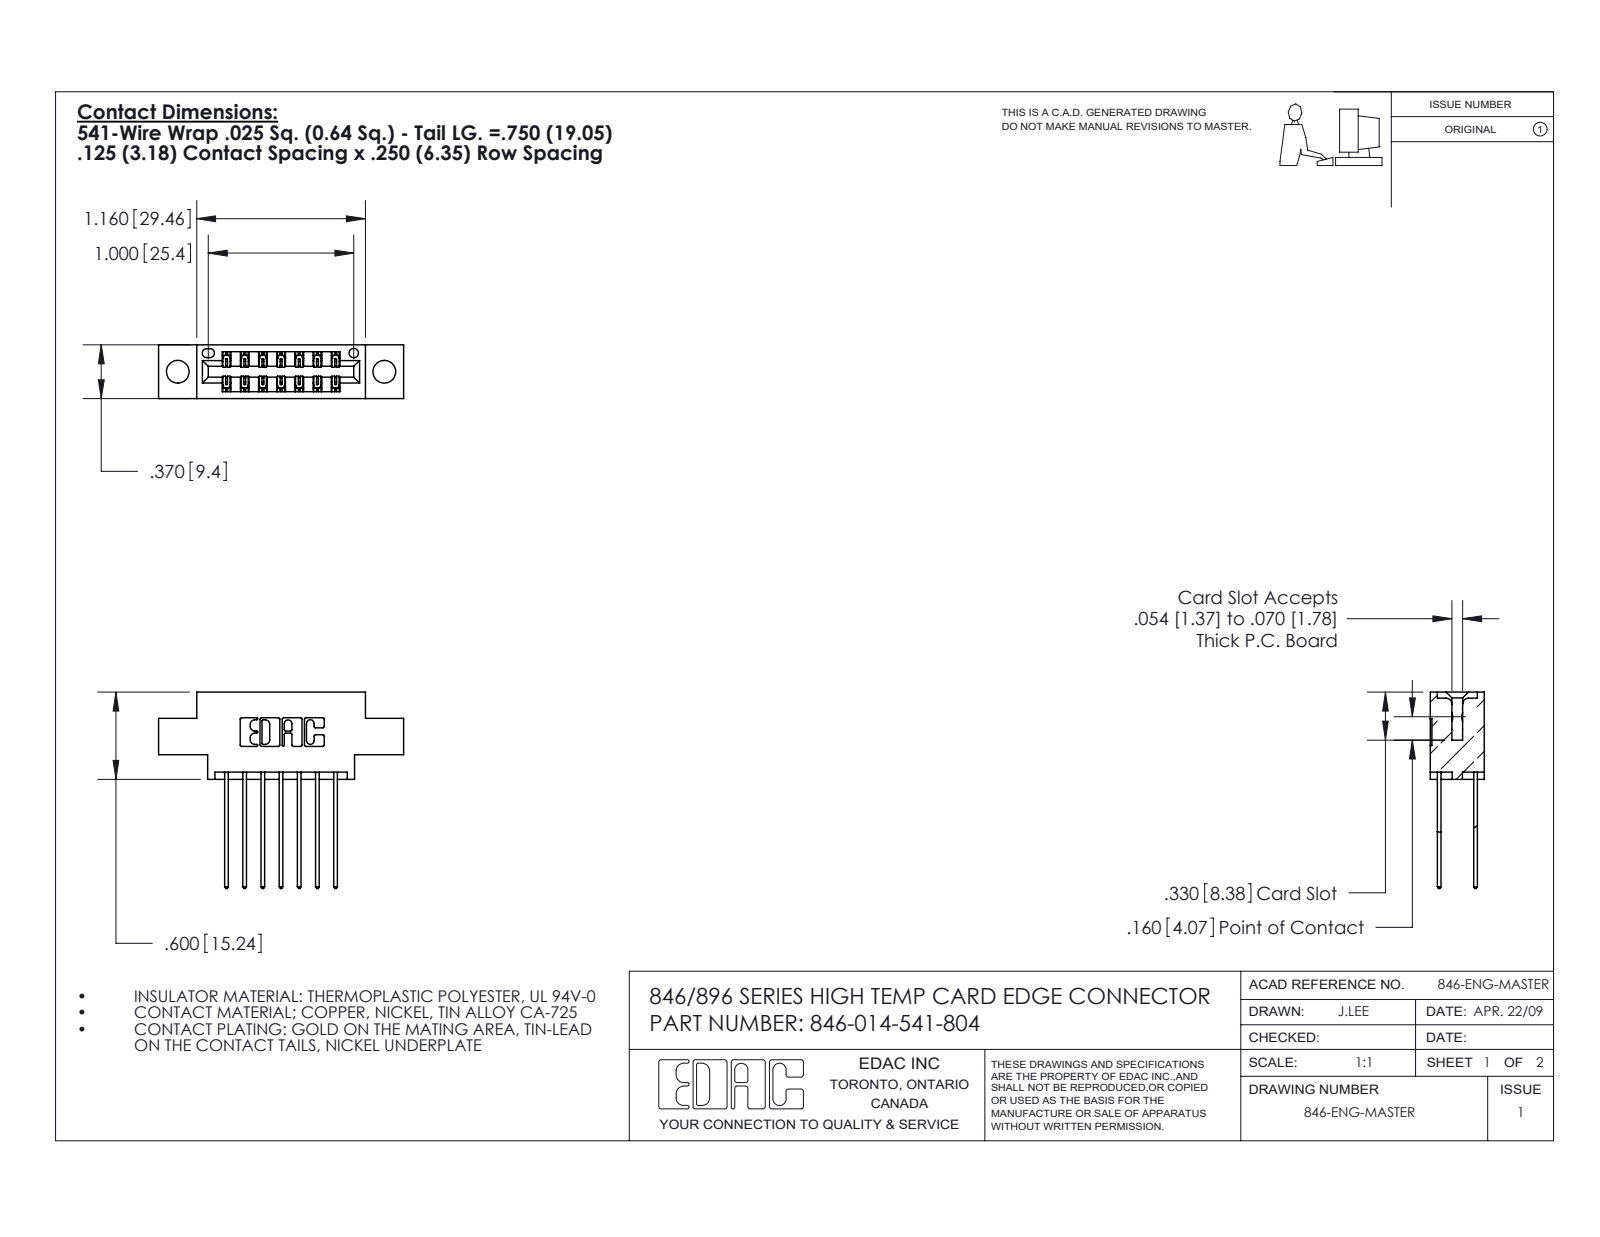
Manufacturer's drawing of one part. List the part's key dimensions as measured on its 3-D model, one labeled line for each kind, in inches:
Part name (STEP PRODUCT): 346-014-541-804; 345-292-001_345-293-141; 346 Part_0.170 Offset - 0.156 Dia-TH
STEP written by: SolidWorks 2016 (CONFIG_CONTROL_DESIGN)
Units: inches
Bodies: 10 solids, 624 faces (420 planar, 204 cylindrical, 0 other)
Overall size (bounding box): 1.685 × 1.35 × 0.37
Volume: 0.224 in³ · Surface area: 6.928 in²
Round holes (diameter × count): ⌀0.156 ×2, ⌀0.064 ×1
Partial cylindrical surfaces — rounded edges, fillets, slot ends (radius × count): R0.01 ×22, R0.006 ×16, R0.01 ×14, R0.007 ×6, R0.031 ×6, R0.026 ×3, R0.014 ×2, R0.022 ×2
Main face-to-face distances: 0.25, 0.37, 0.048, 0.322, 0.072, 0.298, 0.025, 0.148, 0.222, 0.1
Hole centre spacings: 0.246, 1.217, 1.42
